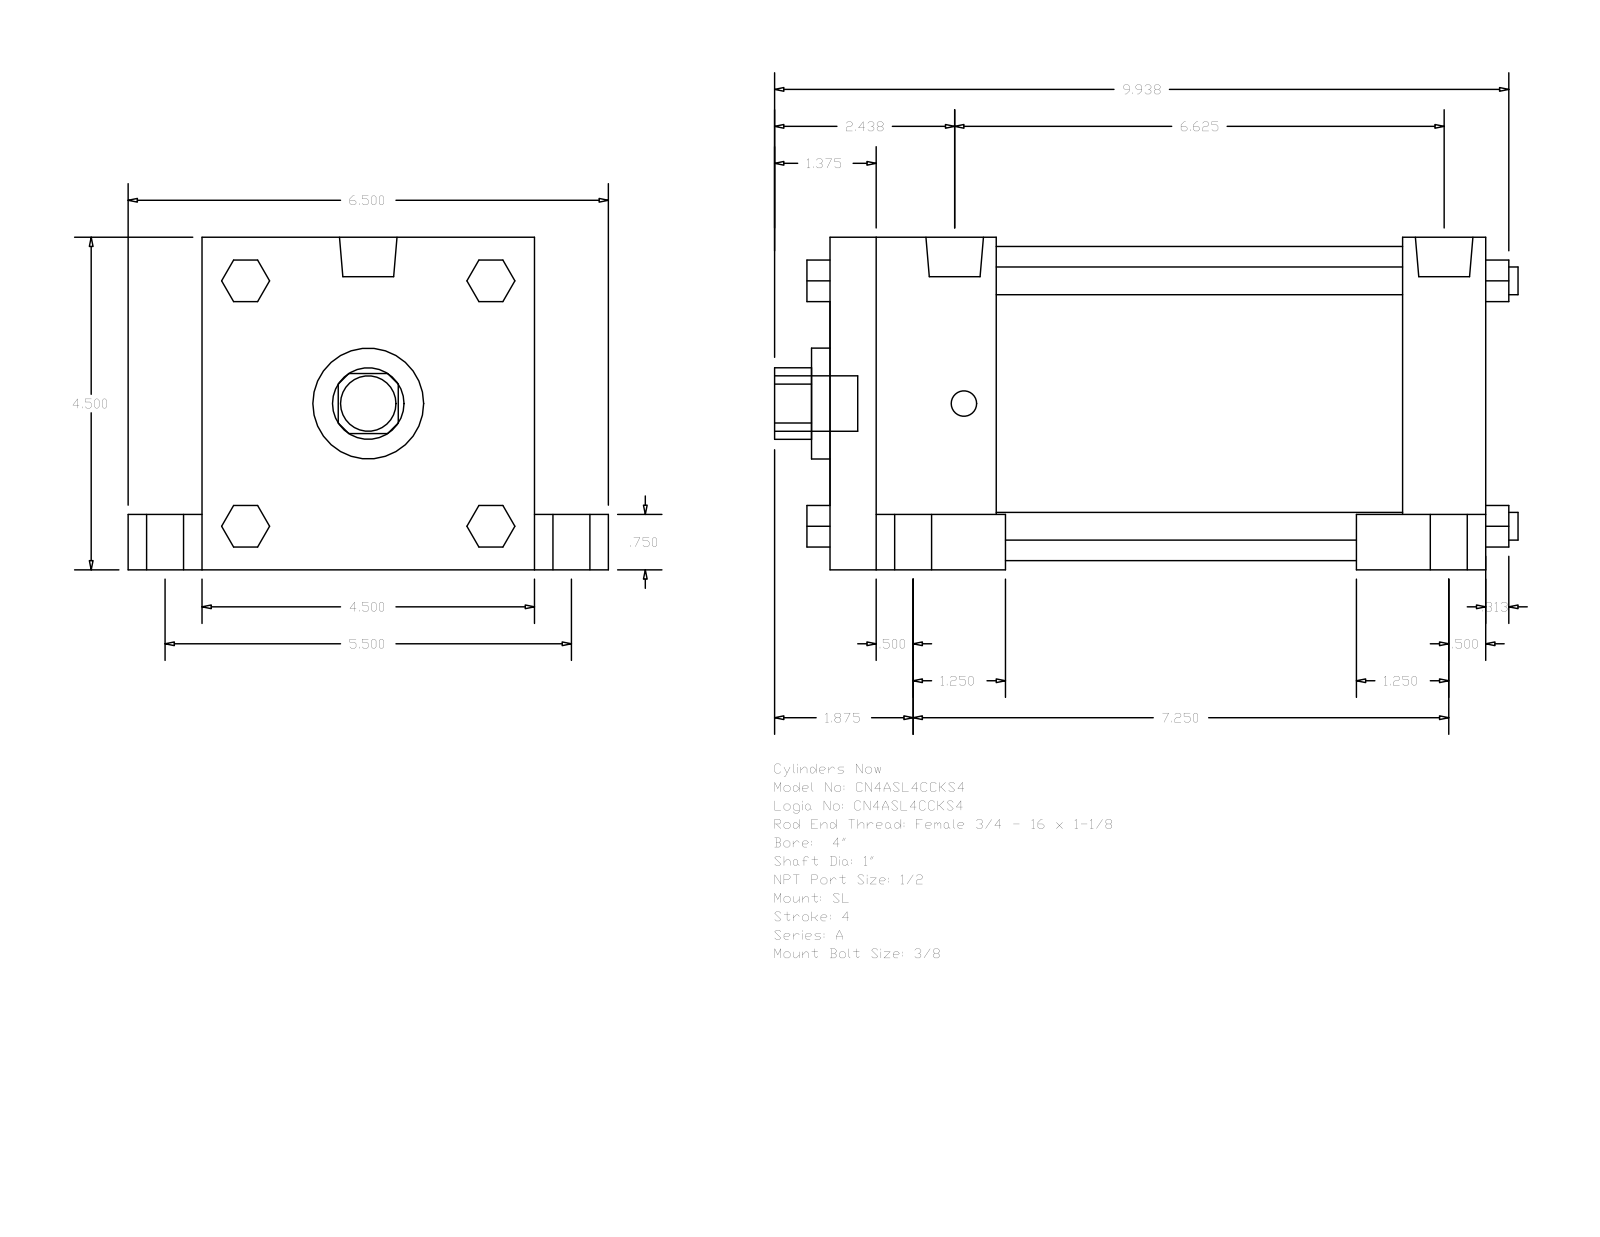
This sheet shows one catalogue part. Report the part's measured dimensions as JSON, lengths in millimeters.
{"part_name": "A_SL__0400_1", "step_written_by": "GSSL Pune (CONFIG_CONTROL_DESIGN)", "units": "millimeters", "bodies": {"solids": 0, "faces": 150, "planar": 114, "cylindrical": 36, "other": 0}, "overall_size": [255.59, 165.1, 114.3], "round_holes": [[25.4, 1], [38.1, 1], [107.95, 1]], "round_bosses_or_shafts": [[19.05, 5], [12.7, 4], [9.53, 4], [8.73, 4], [19.77, 2]], "partial_cylinders_radius": [[12.29, 1]], "face_to_face_distances": [114.3, 225.42, 139.7, 28.57, 57.15, 168.27, 196.85, 19.05, 25.4, 95.25]}
